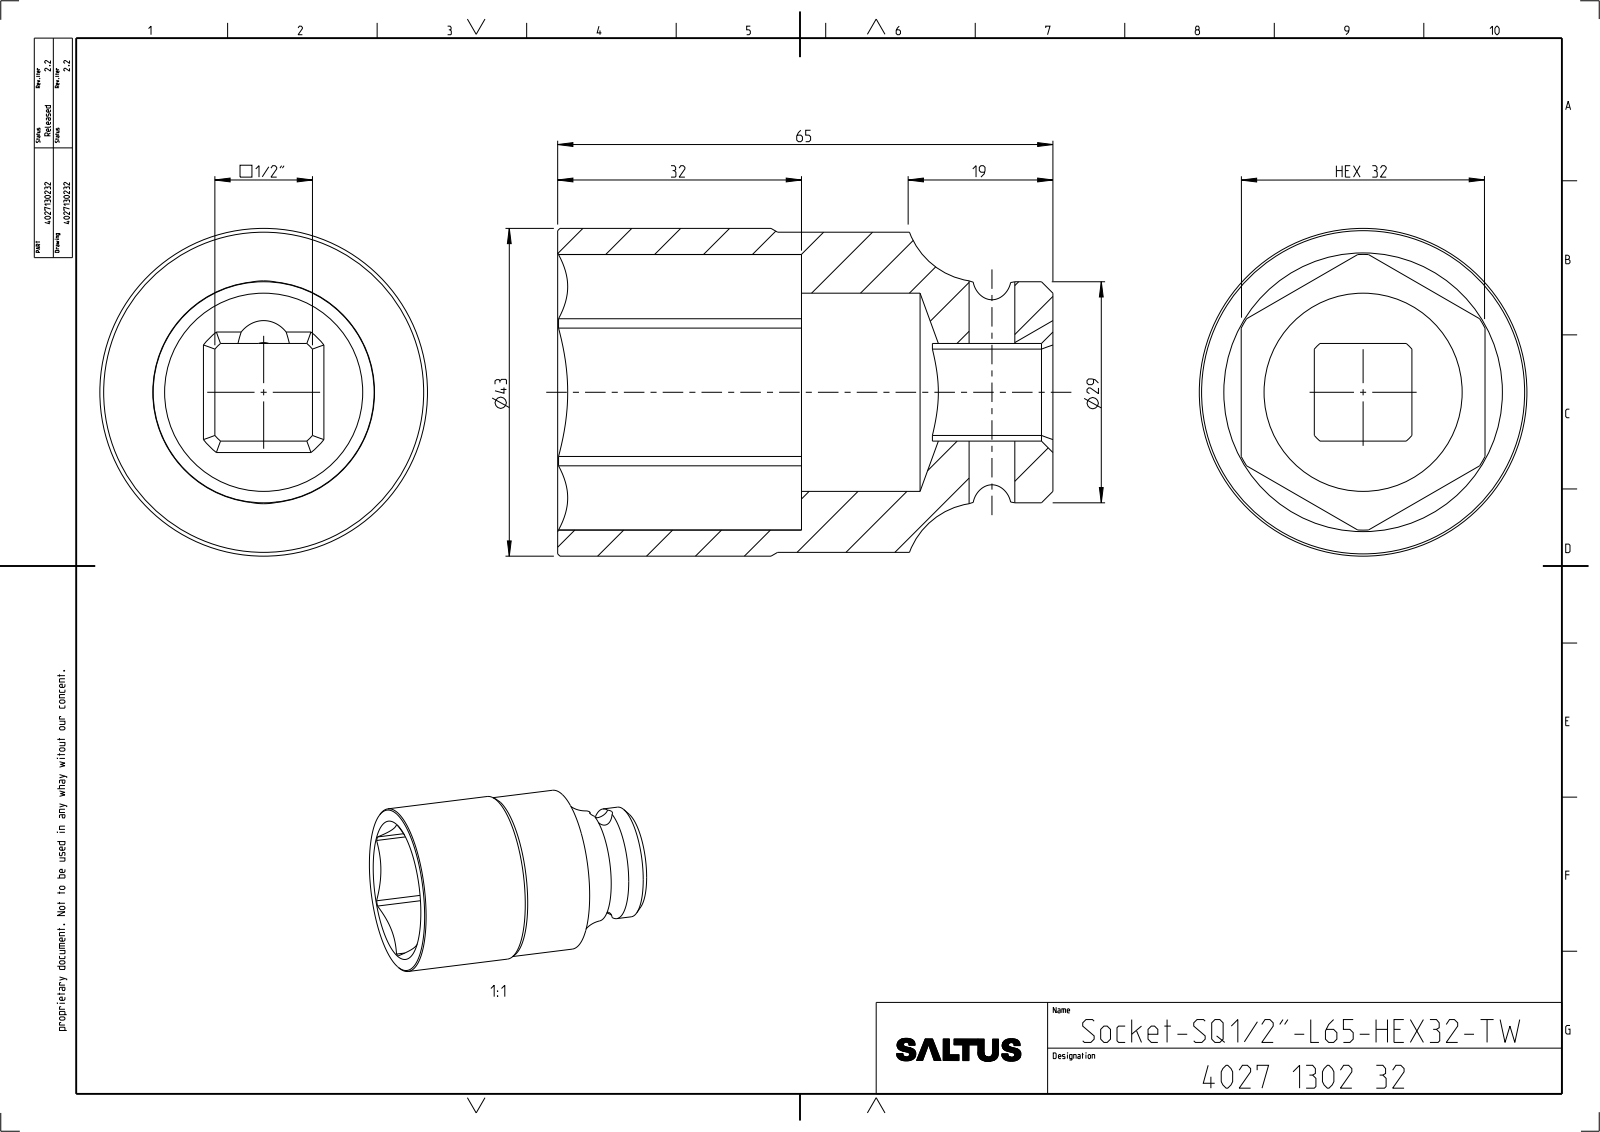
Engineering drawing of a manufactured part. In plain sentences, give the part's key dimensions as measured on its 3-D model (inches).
The part is named "4027130232". Its 3-D file was written by "CREO PARAMETRIC BY PTC INC, 2022414 (CONFIG_CONTROL_DESIGN)". It is 1 solid with 59 faces: 18 planar, 23 cylindrical and 18 other. Overall it measures 2.559 by 1.693 by 1.693 inches. Its volume is 2.376 cubic inches and its surface area 24.39 square inches. Round holes: 1 of diameter 0.236, 1 of diameter 1.024. Round bosses or shafts: 1 of diameter 1.693, 1 of diameter 1.654, 1 of diameter 1.142. Partial cylindrical surfaces (rounded edges, fillets, slot ends): 1 of radius 0.157, 1 of radius 0.337, 1 of radius 0.712. The main face-to-face distances are 1.26, 0.378, 0.882, 1.299, 2.559, 0.505.
